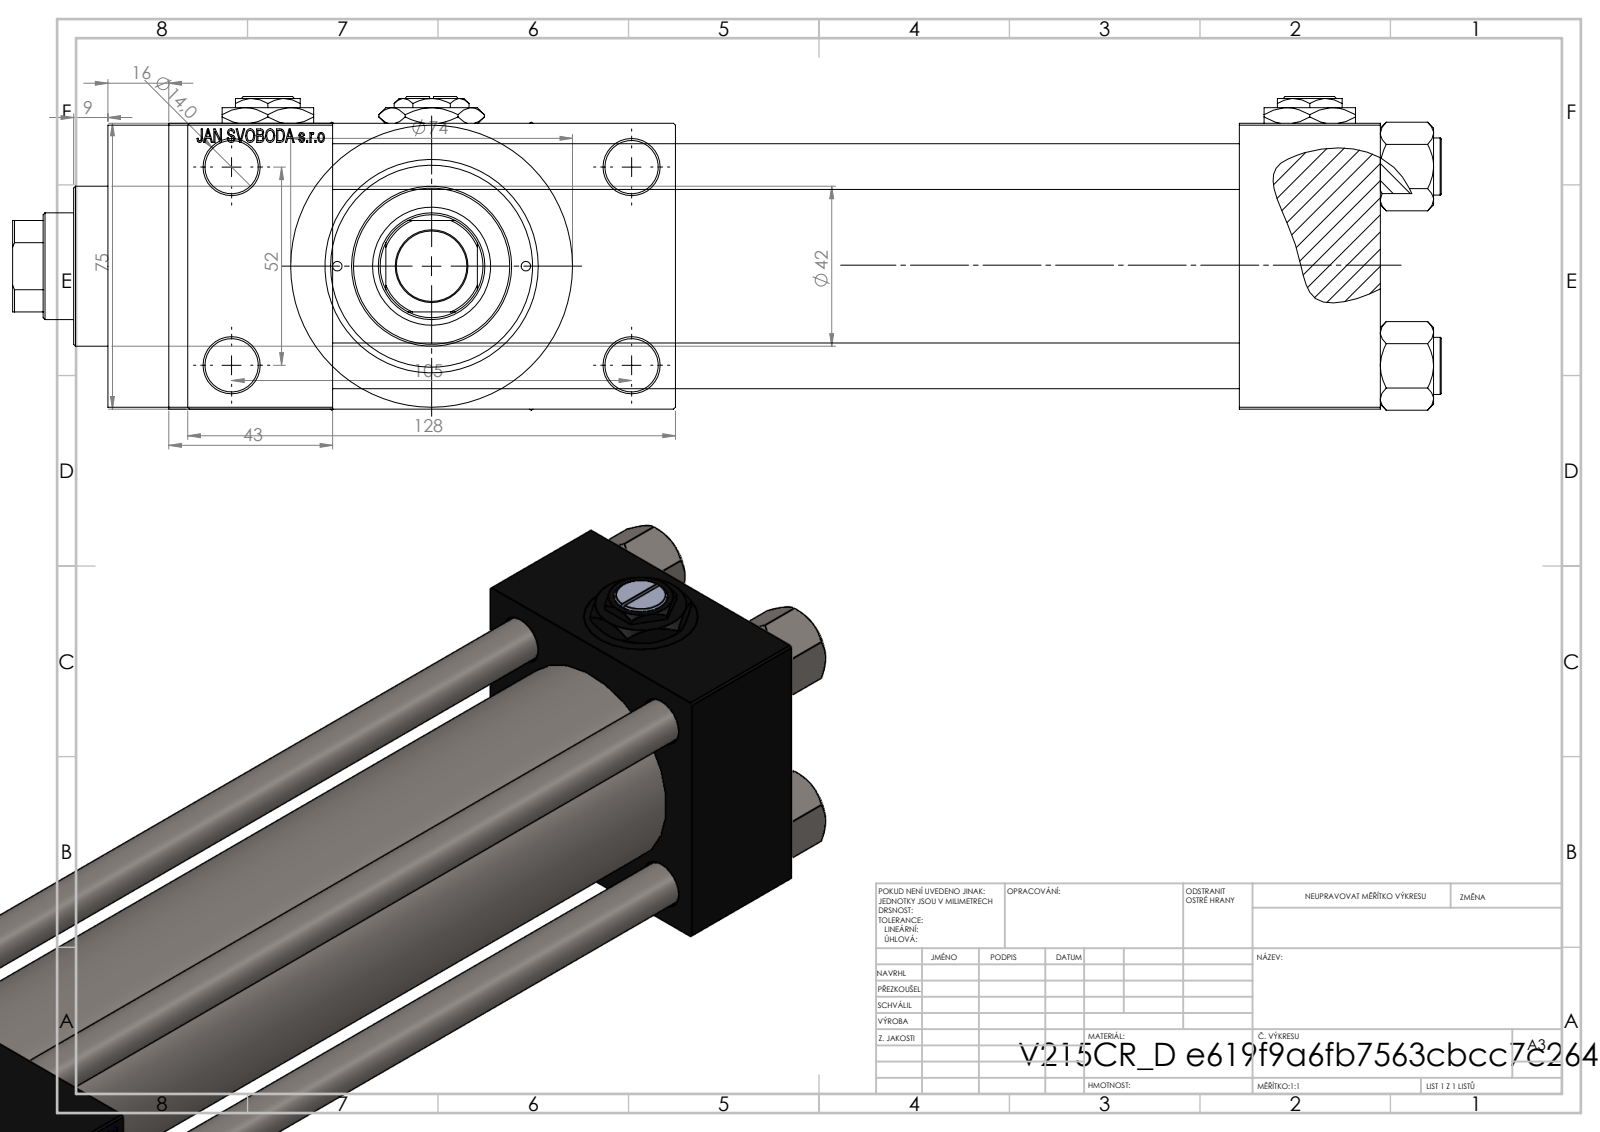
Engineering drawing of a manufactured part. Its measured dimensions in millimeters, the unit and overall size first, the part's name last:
Units: millimetres
Overall size (bounding box): 375 × 128 × 82.27
Round holes (diameter × count): ⌀12 ×4, ⌀14 ×4, ⌀20.96 ×4, ⌀30 ×4, ⌀7 ×3, ⌀2.5 ×2, ⌀18.5 ×1, ⌀28 ×1, ⌀31 ×1, ⌀41 ×1, ⌀50 ×1, ⌀53 ×1
Round bosses / shafts (diameter × count): ⌀15 ×4, ⌀74 ×1, ⌀56 ×1, ⌀42 ×1
Partial cylindrical surfaces — rounded edges, fillets, slot ends (radius × count): R13.5 ×1
Main face-to-face distances: 75, 238, 37, 275, 26.5, 318, 281, 43, 101.5, 16
Hole centre spacings: 26.19, 26.35, 36.98, 38.03, 52.3, 57.22, 58.43, 58.59
Volume: 1 084 000 mm³ · Surface area: 277 696 mm²
Bodies: 13 solids, 1212 faces (547 planar, 103 cylindrical, 562 other)
Part name (STEP PRODUCT): V215CR_D_TYCINKA; V215CR_D_Body; NUT_M5_D; Zatka_pro_OIL_PORT (+2 more)
STEP written by: SolidWorks 2019 (CONFIG_CONTROL_DESIGN)
